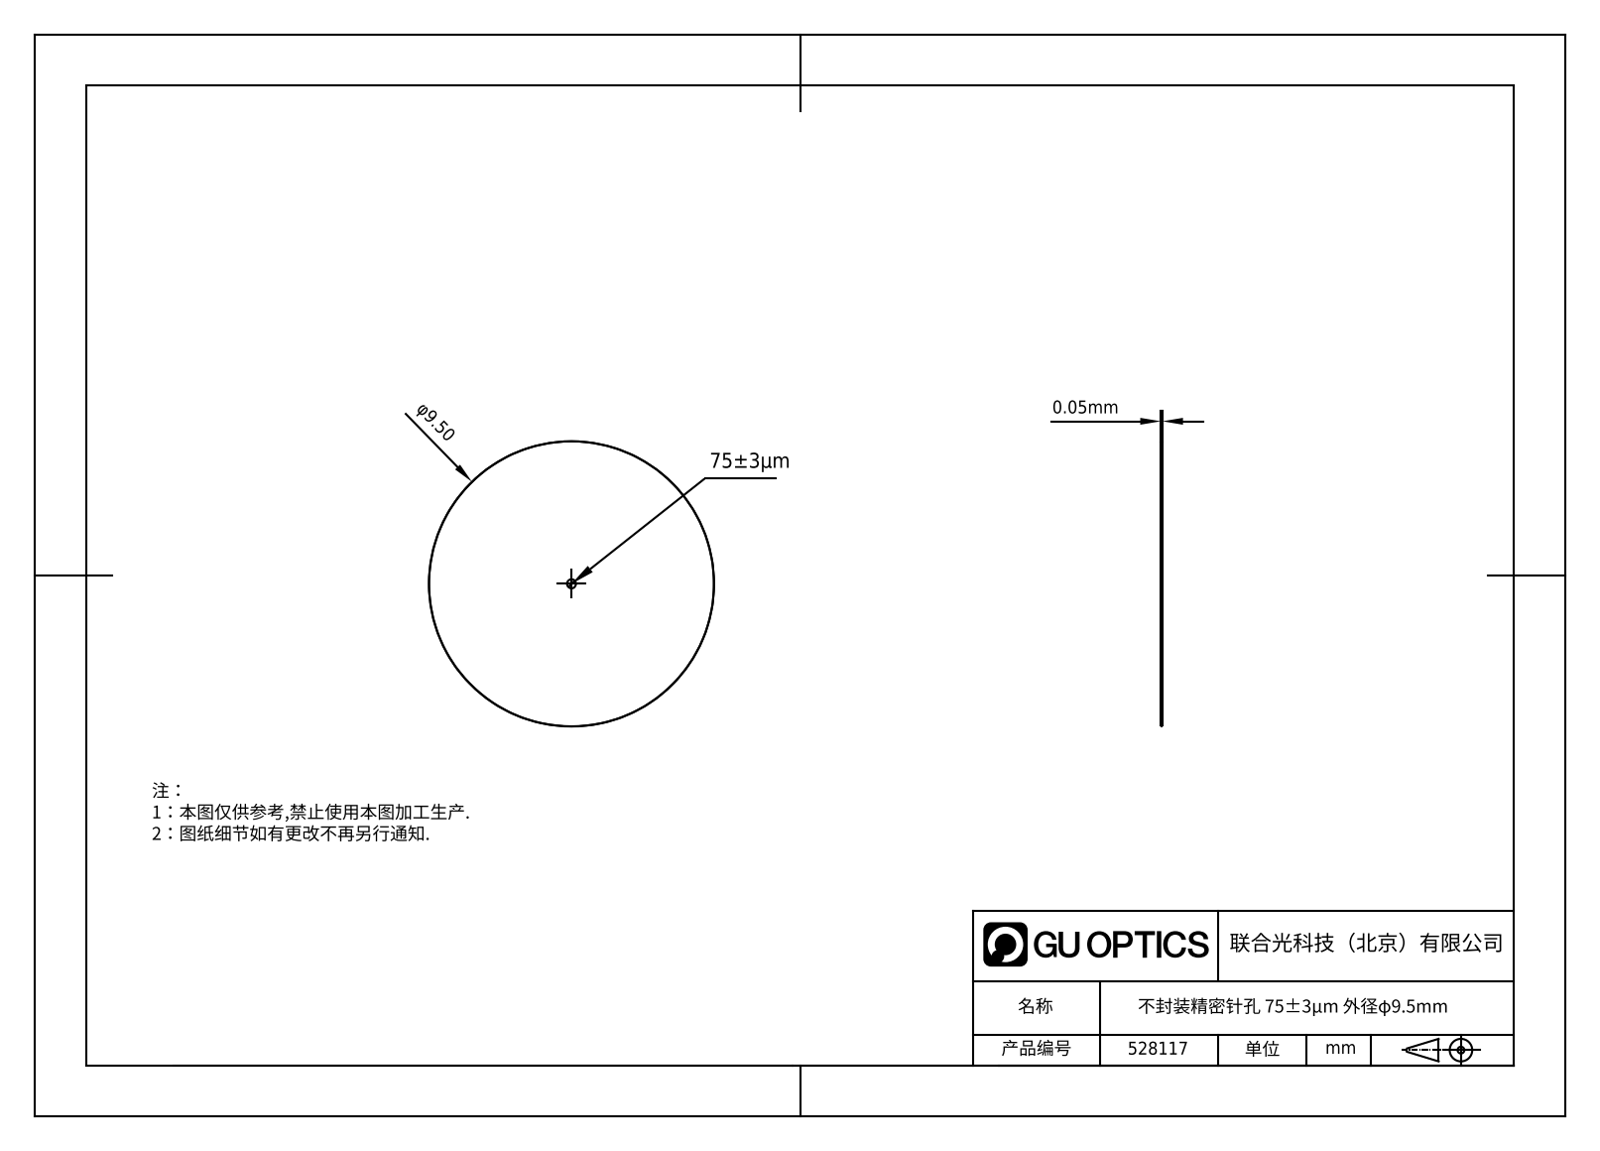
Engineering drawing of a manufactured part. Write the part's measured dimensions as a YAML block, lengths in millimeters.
part_name: "1.5.3.9-ZXO-9.5-75"
step_written_by: "SolidWorks 2021 (CONFIG_CONTROL_DESIGN)"
units: millimeters
bodies: {solids: 1, faces: 6, planar: 2, cylindrical: 4, other: 0}
overall_size: [9.5, 9.5, 0.05]
volume: 4
surface_area: 143
round_bosses_or_shafts:
  - {diameter: 9.5, count: 1}
